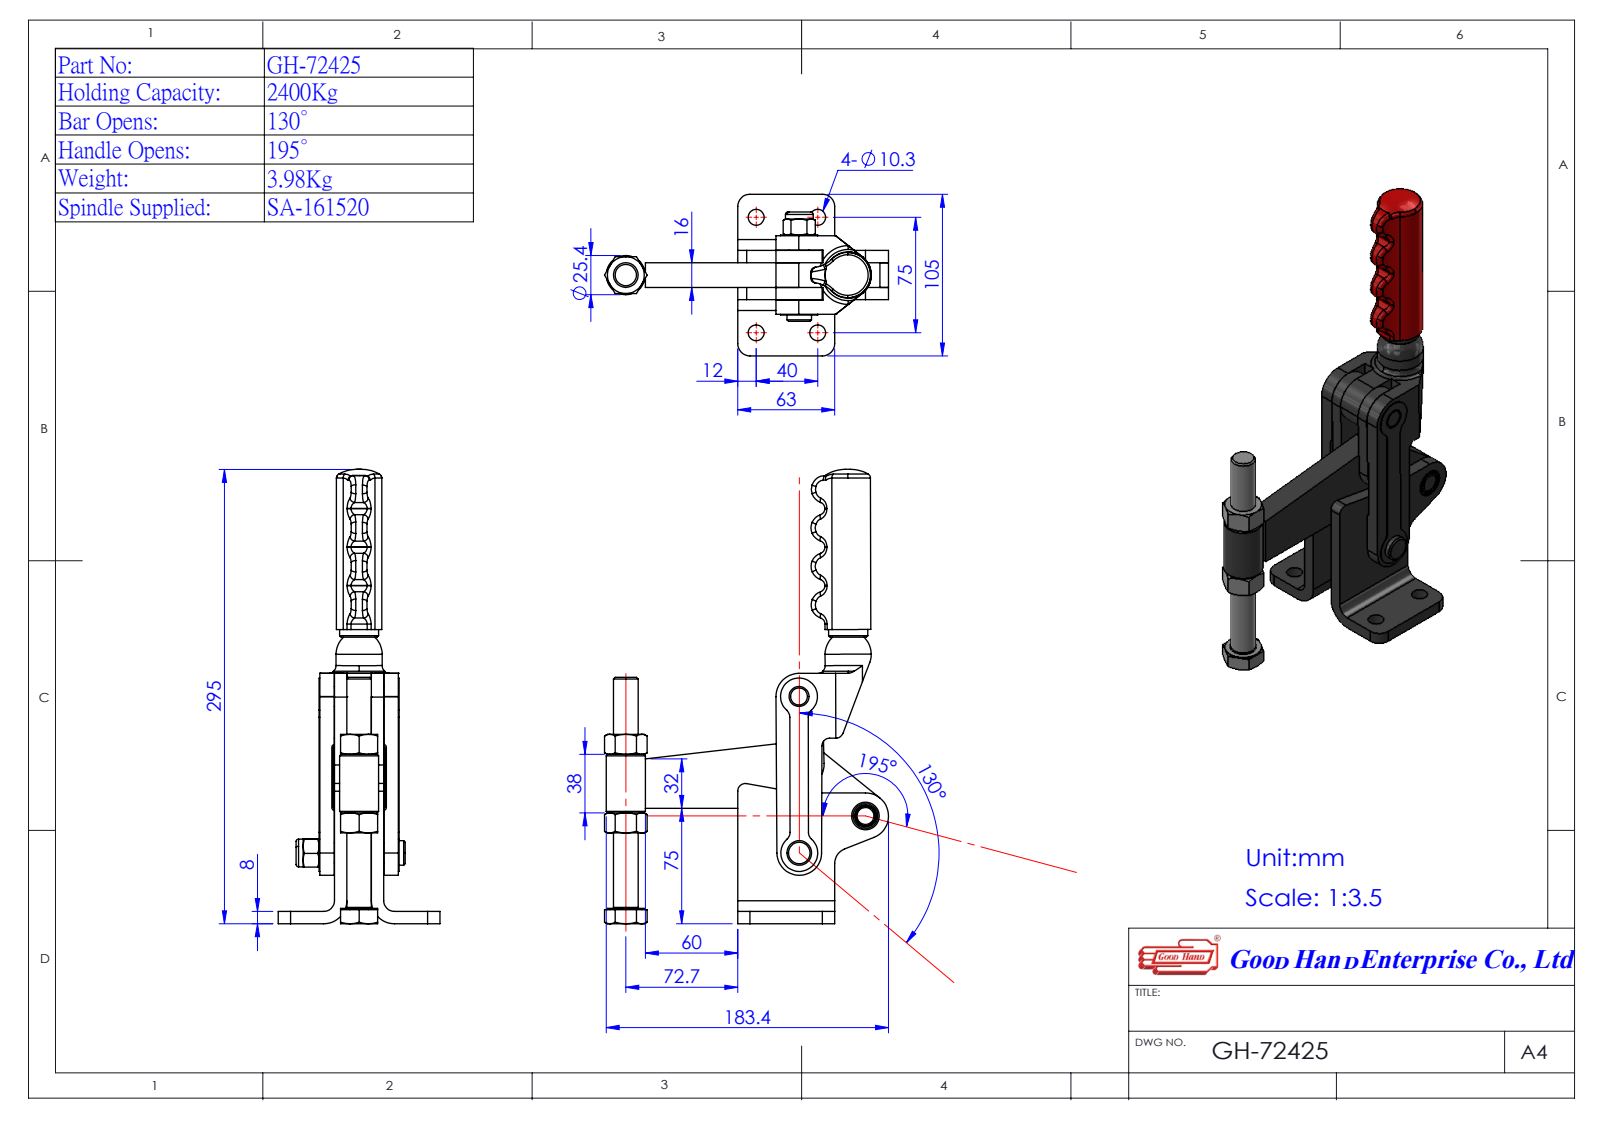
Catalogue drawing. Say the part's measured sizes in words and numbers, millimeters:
The part is named "Group4^GH-72425(簡化)-1; Continuous Thread Hexagon Head Bolt_A_JIS-1^GH-72425(簡化)-1; Group3^GH-72425(簡化)-1; Group2^GH-72425(簡化)-1 (+2 more)". Its 3-D file was written by "SolidWorks 2016 (AUTOMOTIVE_DESIGN)". It is 6 solids with 300 faces: 128 planar, 113 cylindrical and 59 other. Overall it measures 295.07 by 184.56 by 105 millimeters. Its volume is 540 663 cubic millimeters and its surface area 135 627 square millimeters. Round holes: 4 of diameter 9, 4 of diameter 10.3, 1 of diameter 16. Round bosses or shafts: 2 of diameter 25.4, 1 of diameter 30, 1 of diameter 24, 1 of diameter 16, 1 of diameter 15. Partial cylindrical surfaces (rounded edges, fillets, slot ends): 7 of radius 4.1, 7 of radius 15, 4 of radius 6, 4 of radius 8, 4 of radius 9, 3 of radius 5, 2 of radius 7, 2 of radius 12. The main face-to-face distances are 8, 24, 16, 32, 8.15, 24.15, 32.15, 9.35, 9.5, 17.5. The hole center spacings are 39, 75, 84.53, 92.63, 129.26, 44, 49.24, 53.68.
